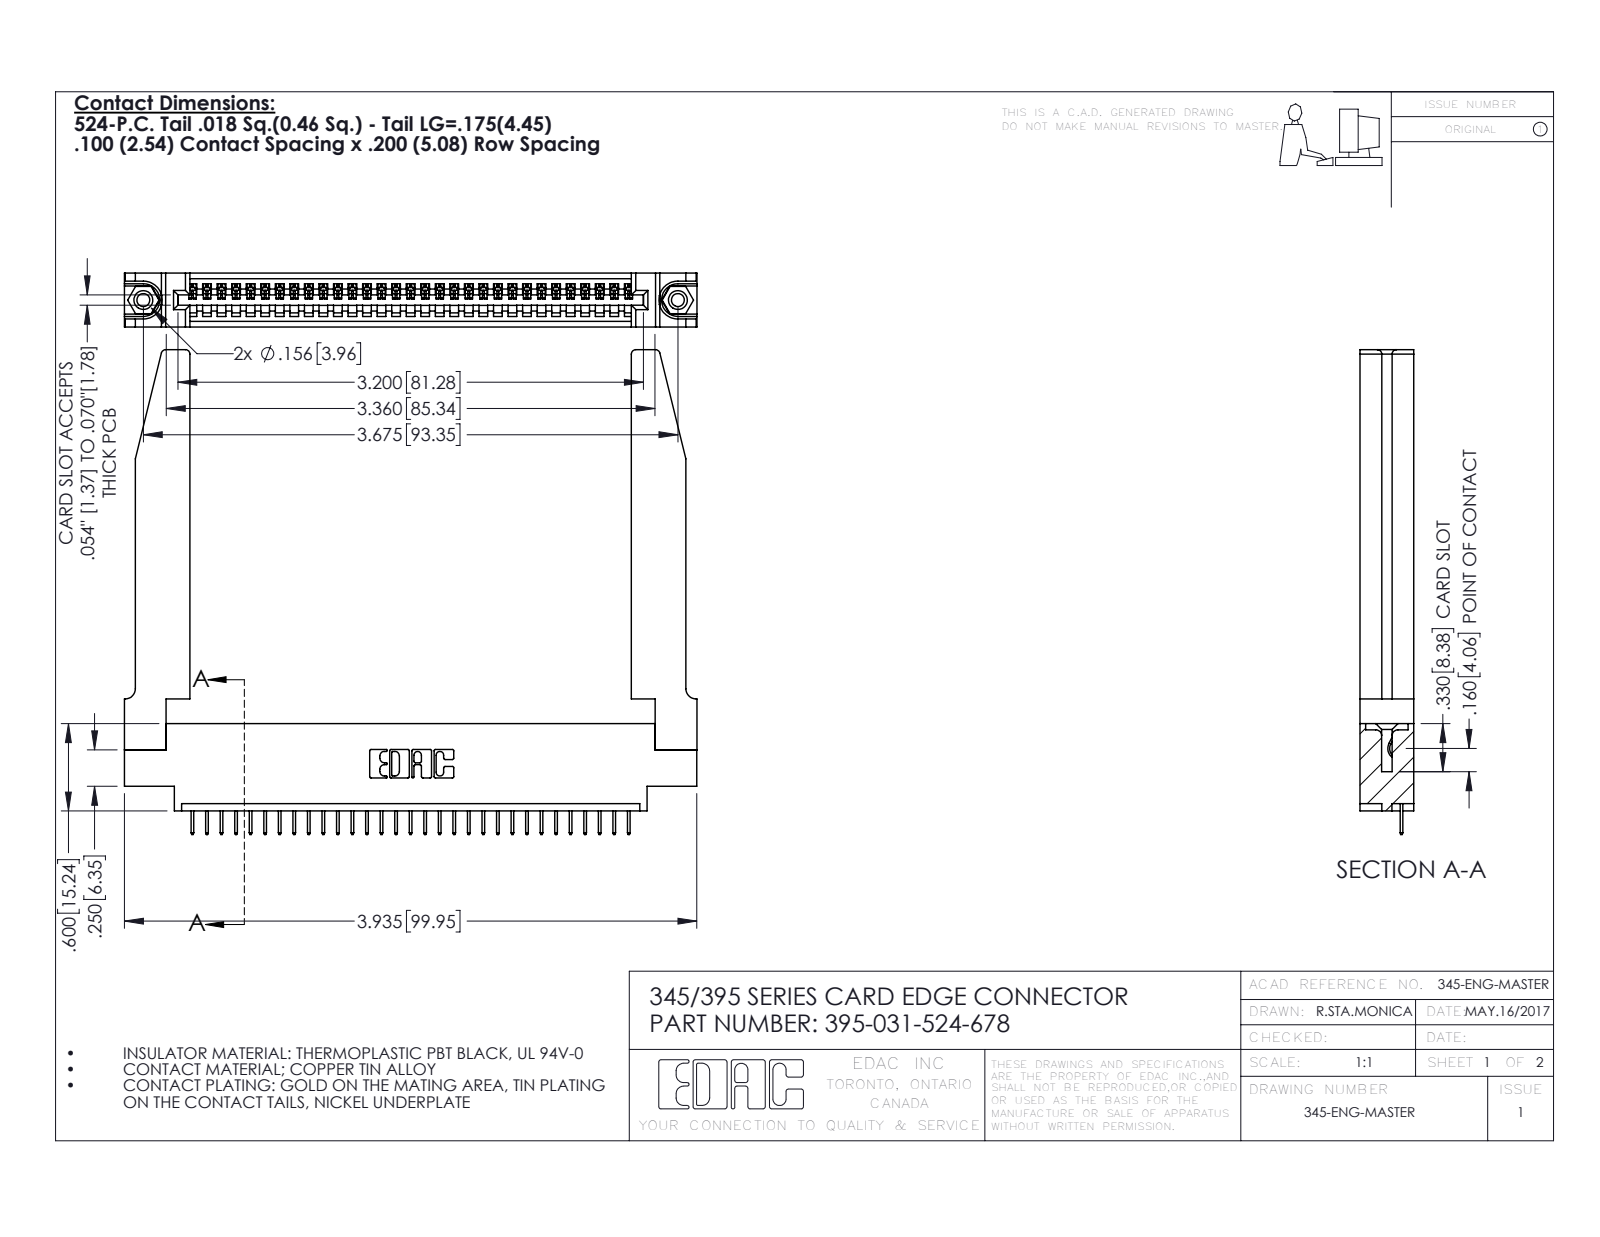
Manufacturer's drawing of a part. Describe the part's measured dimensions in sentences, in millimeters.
The part is named "345-250-001_345-250-001-102; 395-031-524-678; 345-292-001_345-293-124; 345-220-078_345-220-078 (+1 more)". Its 3-D file was written by "SolidWorks 2016 (CONFIG_CONTROL_DESIGN)". It is 36 solids with 2286 faces: 1652 planar, 582 cylindrical and 52 other. Overall it measures 100 by 84.6 by 9.4 millimeters. Its volume is 16 940 cubic millimeters and its surface area 18 620 square millimeters. Round holes: 2 of diameter 2.3, 2 of diameter 3.2, 2 of diameter 4, 1 of diameter 1.6. Round bosses or shafts: 2 of diameter 3.9. Partial cylindrical surfaces (rounded edges, fillets, slot ends): 62 of radius 0.2, 22 of radius 0.3, 8 of radius 0.8, 6 of radius 0.2, 6 of radius 0.8, 3 of radius 0.7, 2 of radius 0.8, 2 of radius 1. The main face-to-face distances are 9.4, 1.8, 7.6, 2.5, 6.9, 0.6, 5.1, 3.8, 3.8, 5.7. The hole center spacings are 6.9, 87.4, 93.3.
